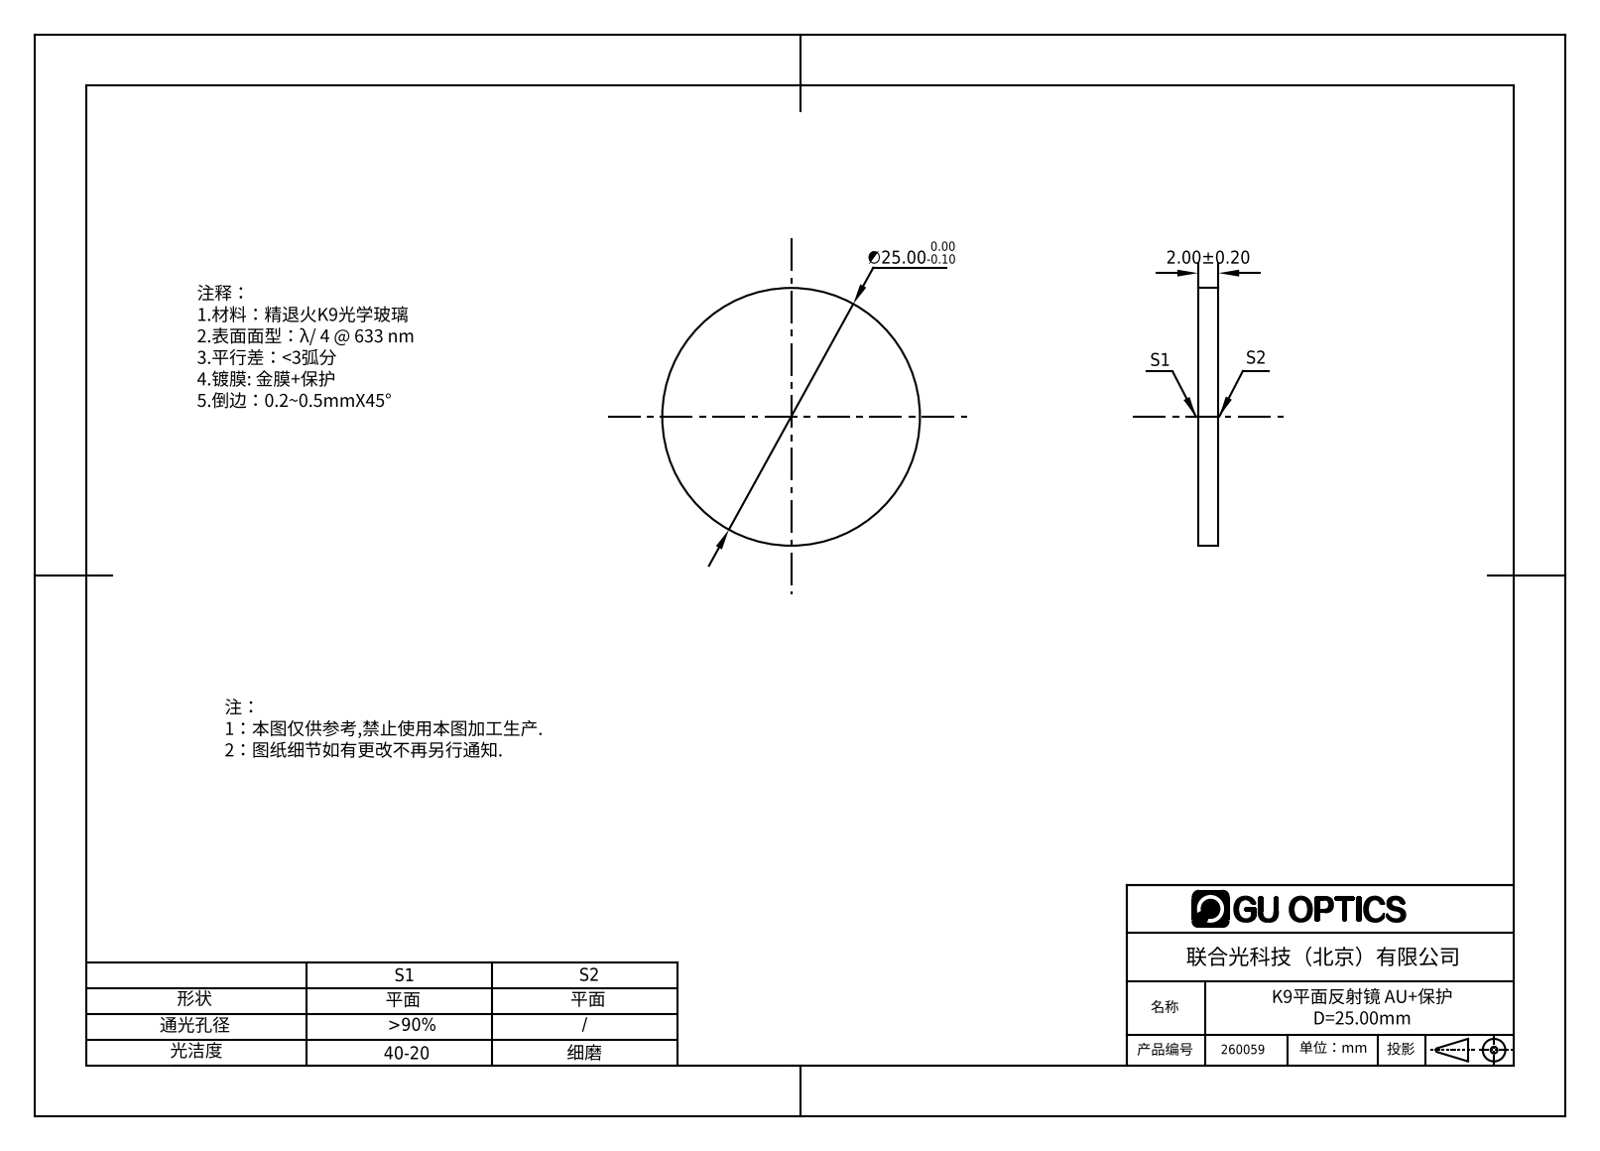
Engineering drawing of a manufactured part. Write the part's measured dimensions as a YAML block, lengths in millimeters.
part_name: "260007"
step_written_by: "SolidWorks 2016 (AUTOMOTIVE_DESIGN)"
units: millimeters
bodies: {solids: 1, faces: 4, planar: 2, cylindrical: 2, other: 0}
overall_size: [25, 25, 2]
volume: 982
surface_area: 1139
round_bosses_or_shafts:
  - {diameter: 25, count: 1}
face_to_face_distances: [2]
